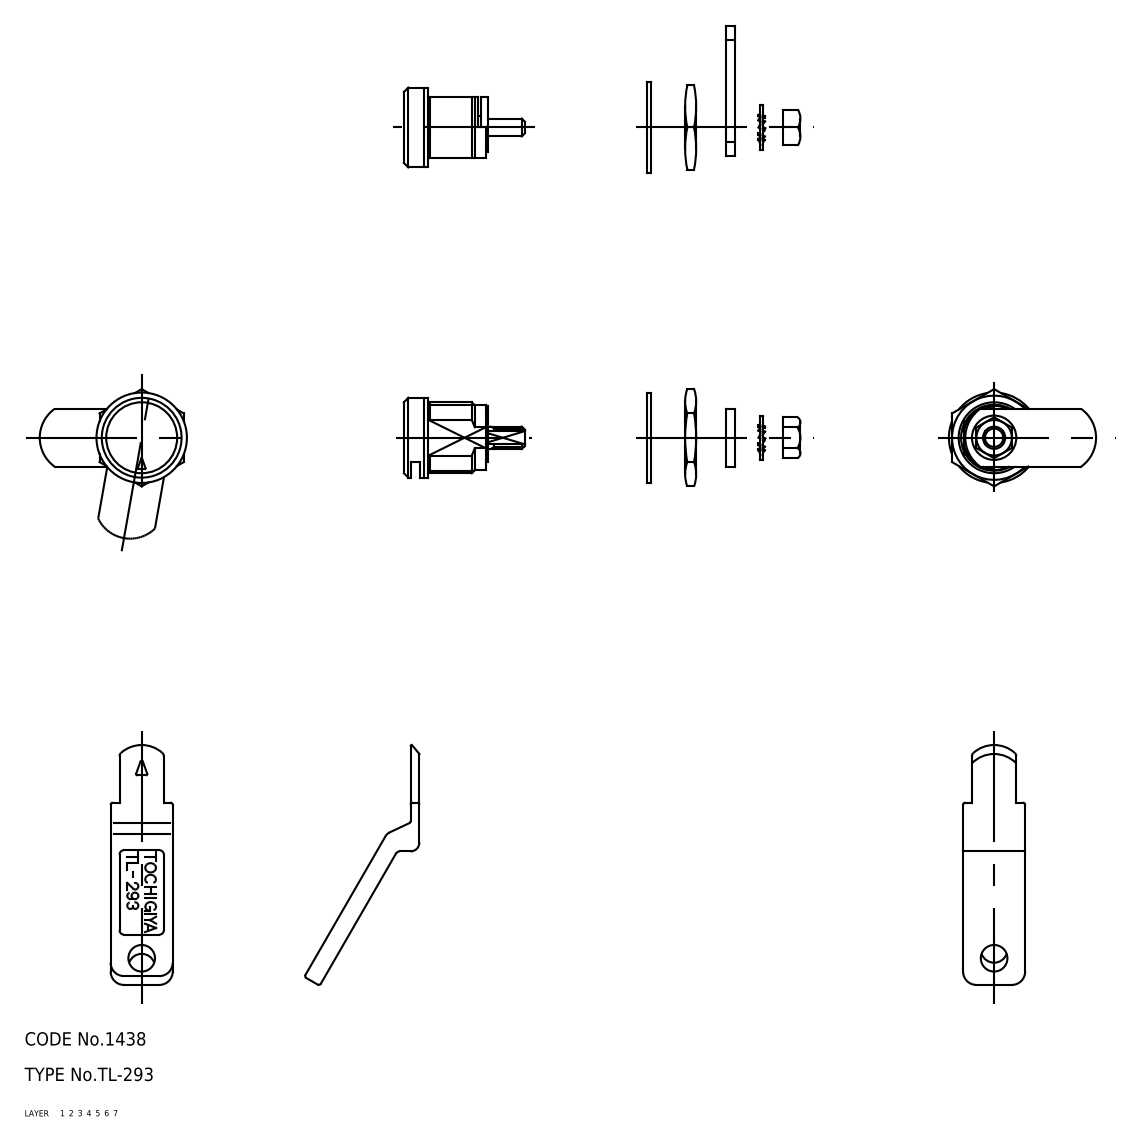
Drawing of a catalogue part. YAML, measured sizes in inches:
part_name: "lock_2; lock_1; washer_2; washer_1 (+6 more)"
step_written_by: "CADfix (AUTOMOTIVE_DESIGN)"
units: inches
bodies: {solids: 9, faces: 185, planar: 0, cylindrical: 0, other: 185}
overall_size: [3.659, 1.952, 1.307]
volume: 0.462
surface_area: 11.03
